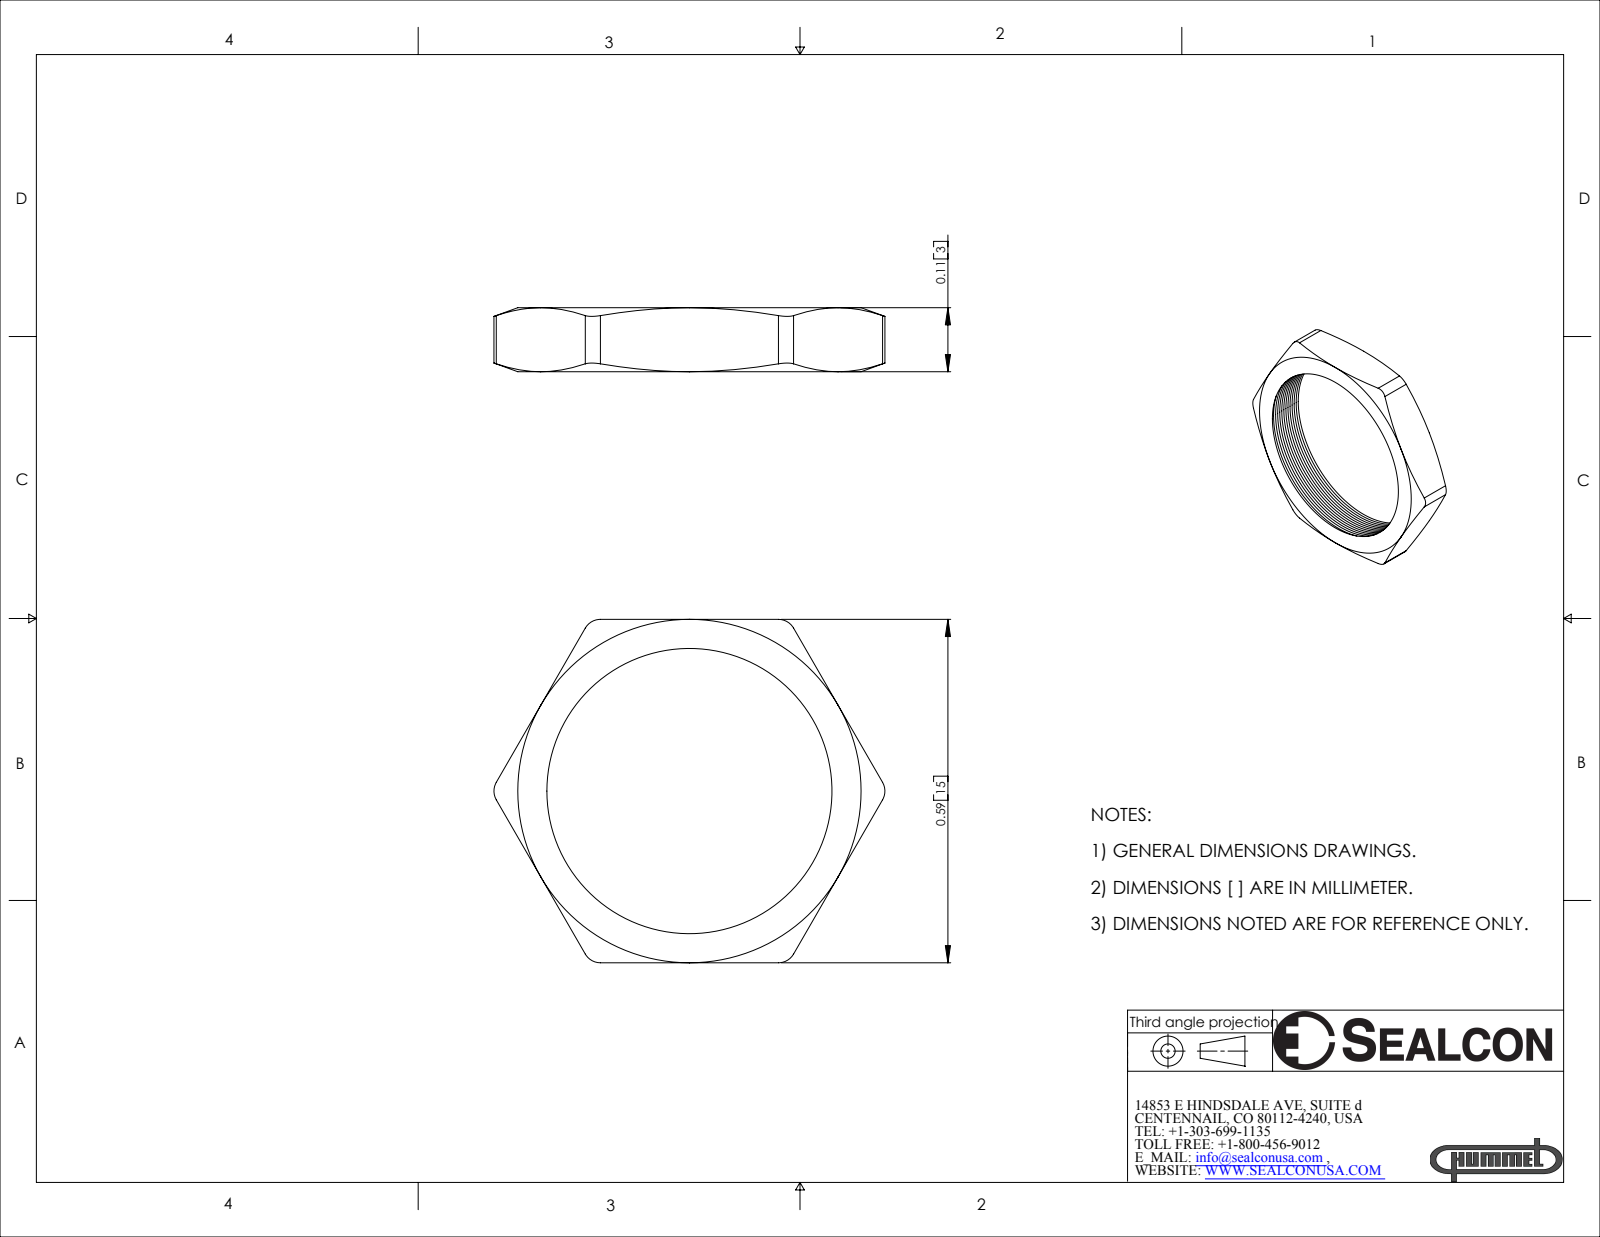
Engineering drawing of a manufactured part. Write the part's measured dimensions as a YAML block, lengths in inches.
part_name: "NP-07-BR"
step_written_by: "SolidWorks 2007 (CONFIG_CONTROL_DESIGN)"
units: inches
bodies: {solids: 1, faces: 83, planar: 8, cylindrical: 7, other: 68}
overall_size: [0.672, 0.59, 0.11]
volume: 0.01
surface_area: 0.767
partial_cylinders:
  - {radius: 0.03, count: 6}
face_to_face_distances: [0.59, 0.11]
